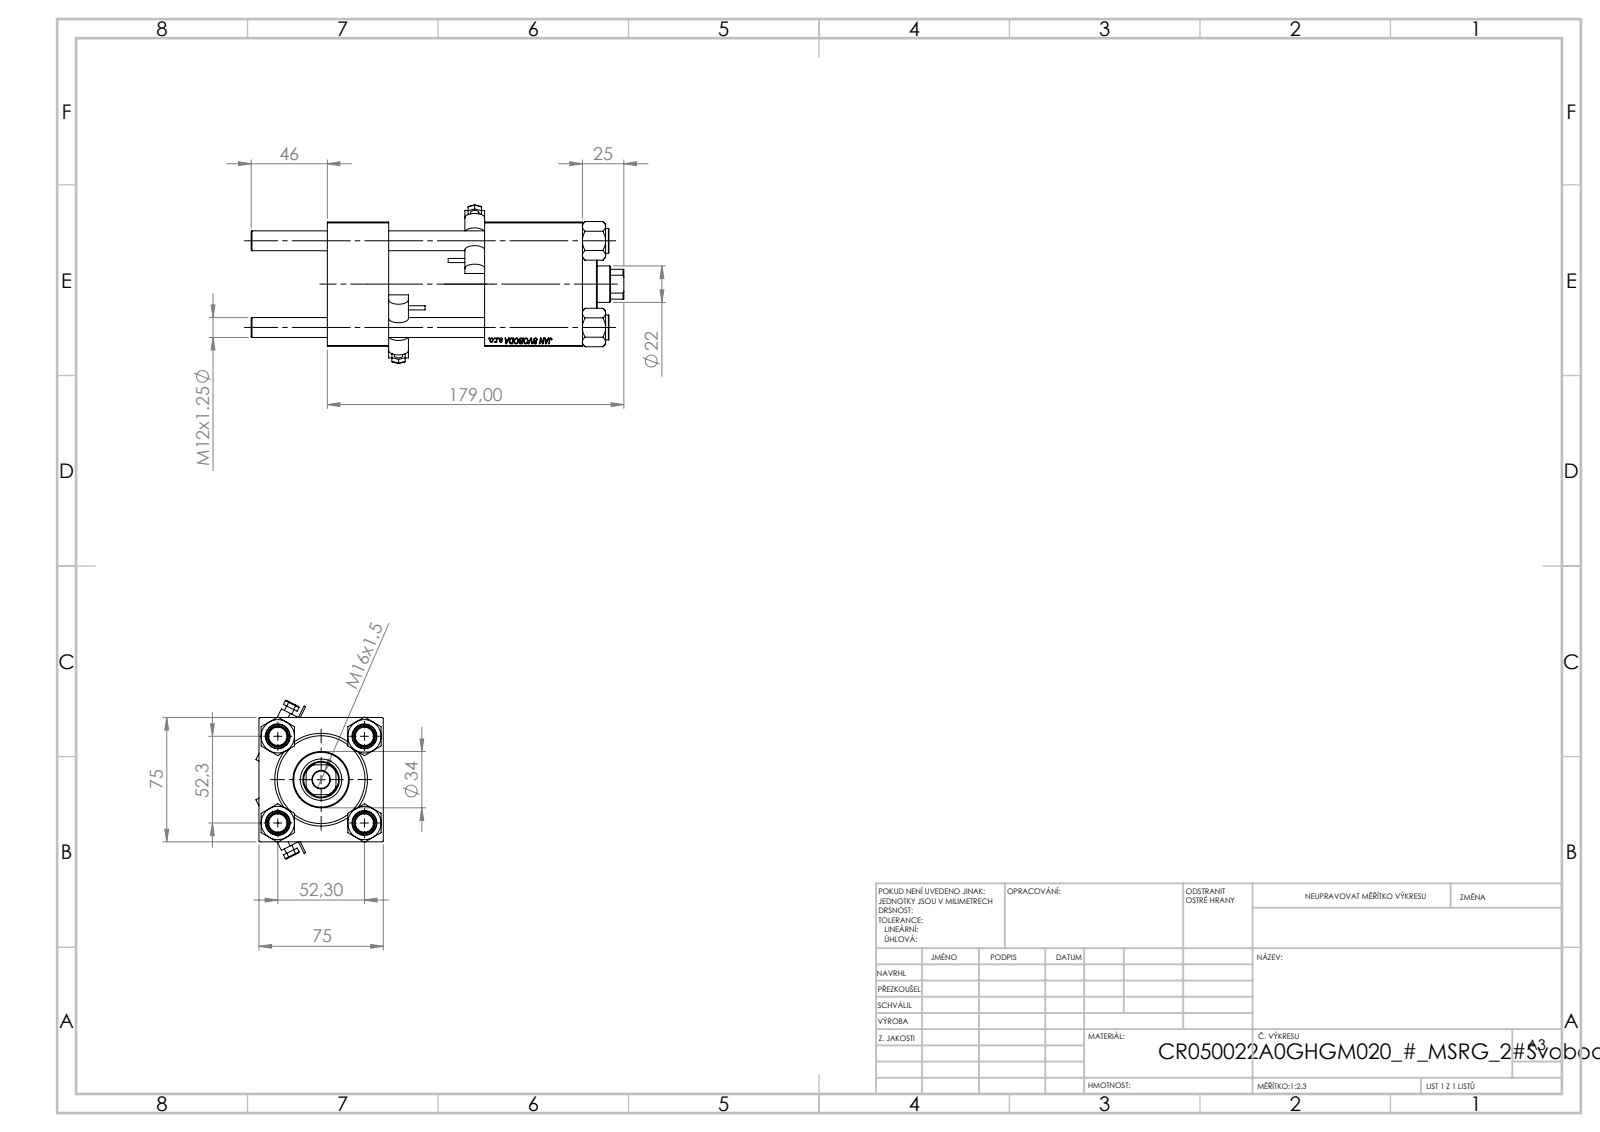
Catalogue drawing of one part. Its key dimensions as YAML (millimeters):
part_name: "V215CR_BODY_A; V215_VC_A; NUT_M5; MSRF_MSRG1 (+2 more)"
step_written_by: "SolidWorks 2019 (CONFIG_CONTROL_DESIGN)"
units: millimeters
bodies: {solids: 13, faces: 1198, planar: 556, cylindrical: 106, other: 536}
overall_size: [225, 95.81, 76.88]
volume: 697465
surface_area: 168236
round_holes:
  - {diameter: 12, count: 4}
  - {diameter: 7, count: 2}
  - {diameter: 20.96, count: 2}
  - {diameter: 30, count: 2}
  - {diameter: 10.5, count: 1}
  - {diameter: 22, count: 1}
  - {diameter: 25, count: 1}
  - {diameter: 41, count: 1}
  - {diameter: 50, count: 1}
  - {diameter: 53, count: 1}
round_bosses_or_shafts:
  - {diameter: 15, count: 4}
  - {diameter: 5, count: 2}
  - {diameter: 2.5, count: 2}
  - {diameter: 56, count: 1}
  - {diameter: 34, count: 1}
partial_cylinders:
  - {radius: 0.5, count: 12}
  - {radius: 6, count: 4}
  - {radius: 10.5, count: 1}
face_to_face_distances: [75, 37, 154, 117, 95, 58, 59, 125.3, 88.3, 30.3]
hole_center_spacings: [36.98, 52.3, 73.96, 93.5]
